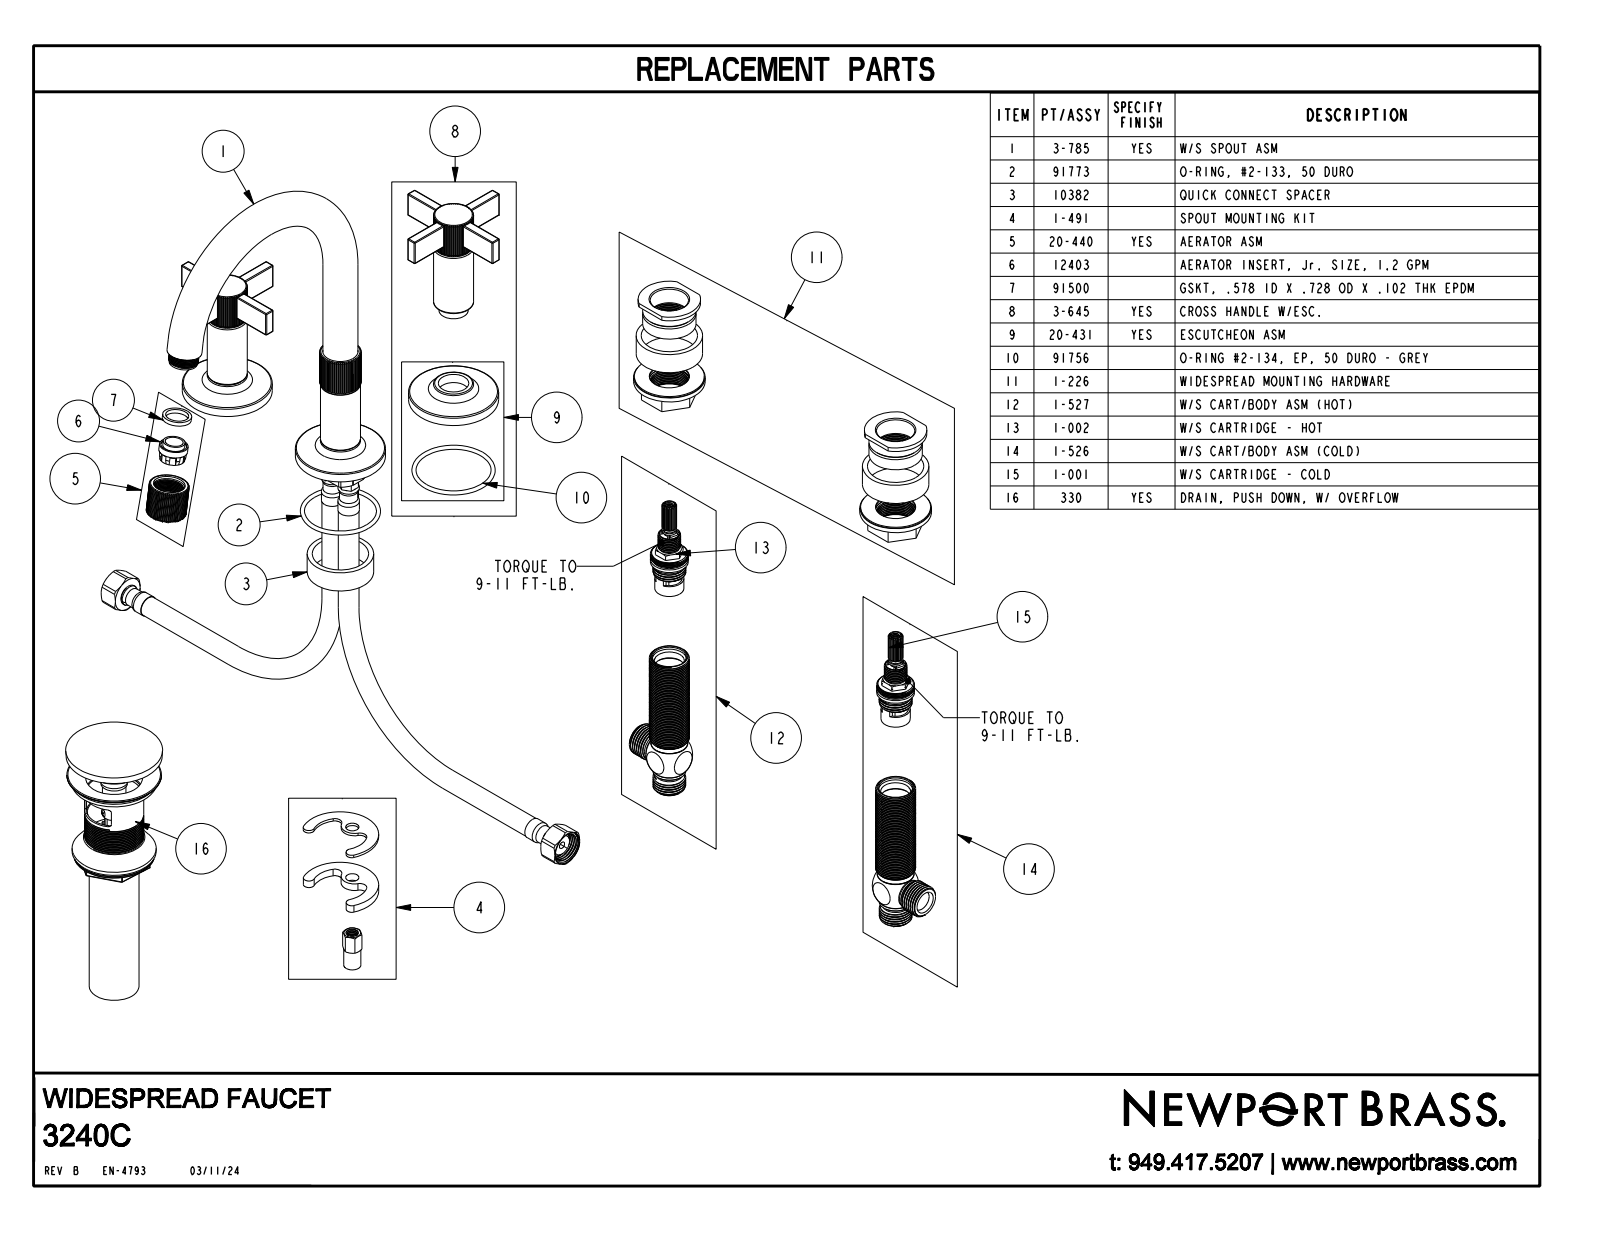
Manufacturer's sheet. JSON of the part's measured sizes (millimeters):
{"part_name": "3240C", "step_written_by": "CREO PARAMETRIC BY PTC INC, 2023134 (CONFIG_CONTROL_DESIGN)", "units": "millimeters", "bodies": {"solids": 3, "faces": 1177, "planar": 673, "cylindrical": 412, "other": 92}, "overall_size": [279.4, 230, 193.5], "volume_mm3": 310000, "surface_area_mm2": 73480, "round_holes": [[14.2, 1], [17.6, 1], [22.4, 1]], "round_bosses_or_shafts": [[57.2, 3], [25.4, 3], [22.2, 2], [21.6, 2], [13.2, 2], [24.6, 1], [11.8, 1]], "partial_cylinders_radius": [[0.5, 40], [7.9, 2], [8.6, 1], [12.7, 1], [13.2, 1]], "face_to_face_distances": [6.4, 203.2, 6.4, 79.9, 63.4, 16.5, 81.3, 17.9, 1.4, 15.8]}
